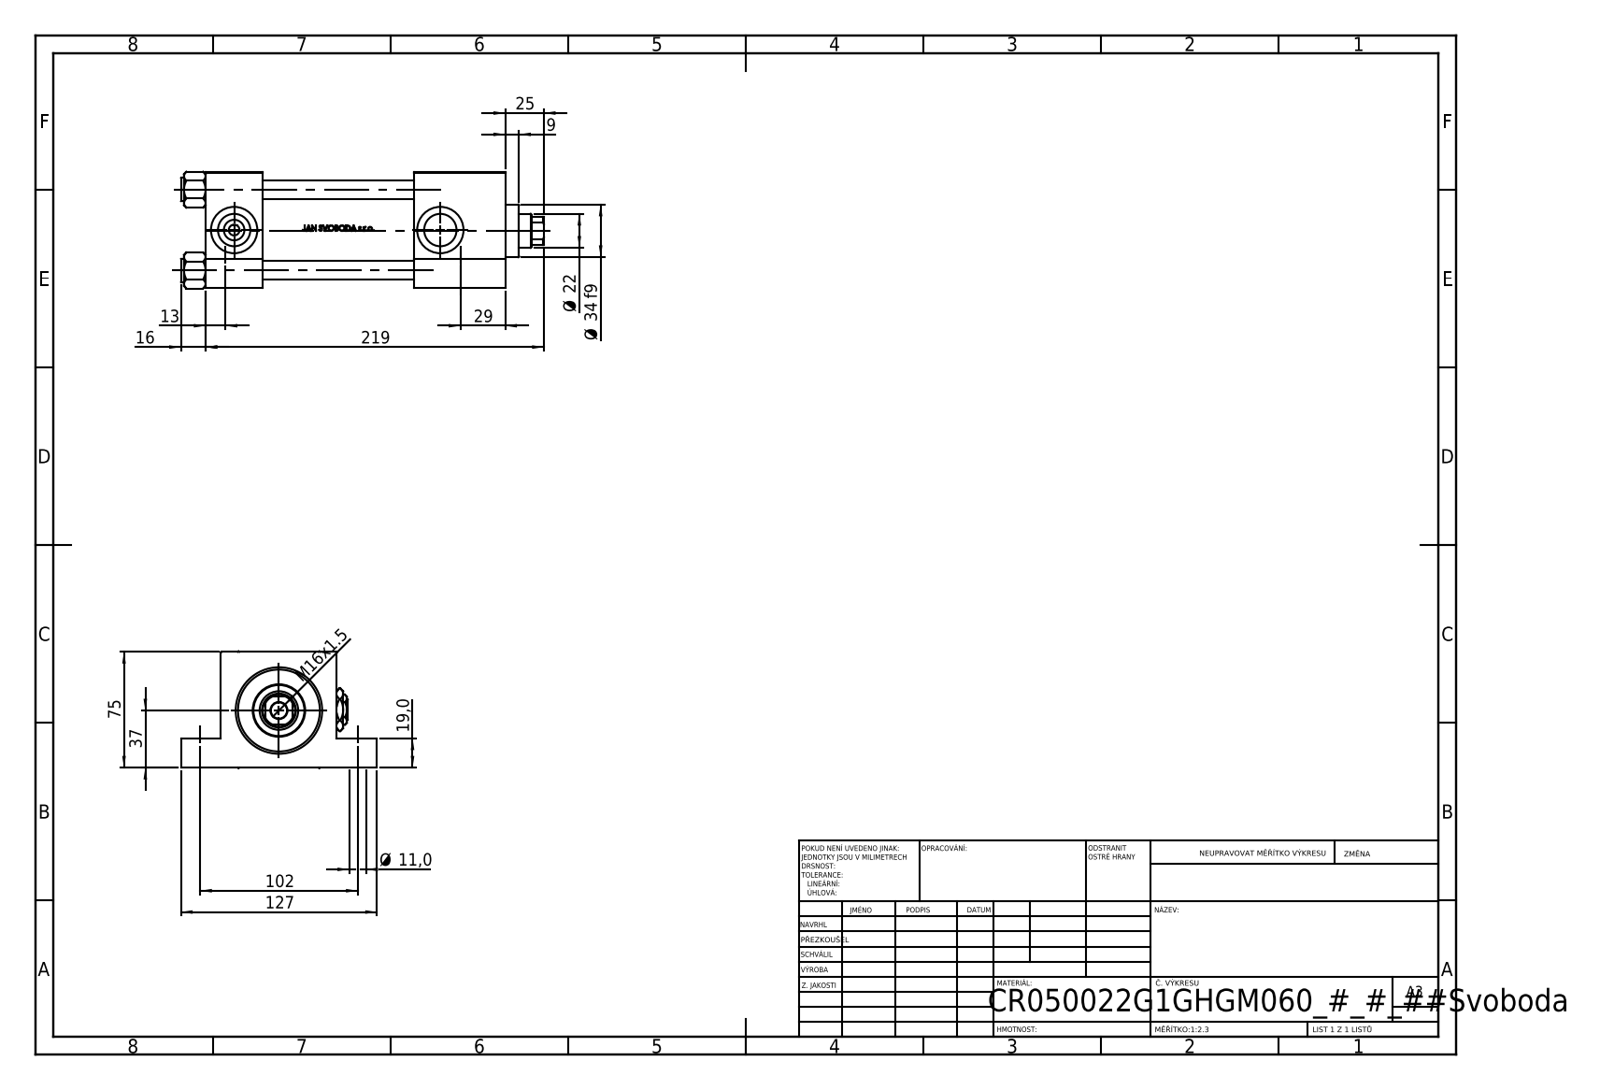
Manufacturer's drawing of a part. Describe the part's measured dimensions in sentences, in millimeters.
The part is named "Zatka_pro_OIL_PORT; NUT_M5_G; V215_VC_A; V215CR_G_Body (+2 more)". Its 3-D file was written by "SolidWorks 2019 (CONFIG_CONTROL_DESIGN)". It is 12 solids with 1134 faces: 454 planar, 128 cylindrical and 552 other. Overall it measures 235 by 127 by 75.54 millimeters. Its volume is 805 684 cubic millimeters and its surface area 183 420 square millimeters. Round holes: 4 of diameter 11, 4 of diameter 12, 2 of diameter 7, 2 of diameter 20.96, 2 of diameter 30, 1 of diameter 10.5, 1 of diameter 22, 1 of diameter 25, 1 of diameter 41, 1 of diameter 50, 1 of diameter 53. Round bosses or shafts: 4 of diameter 15, 1 of diameter 56, 1 of diameter 34. Partial cylindrical surfaces (rounded edges, fillets, slot ends): 1 of radius 10.5. The main face-to-face distances are 75, 37, 194, 157, 19, 56, 135, 98, 59, 26. The hole center spacings are 52.3, 36.63, 37.34, 73.96, 102, 152, 183.05, 133.5.
